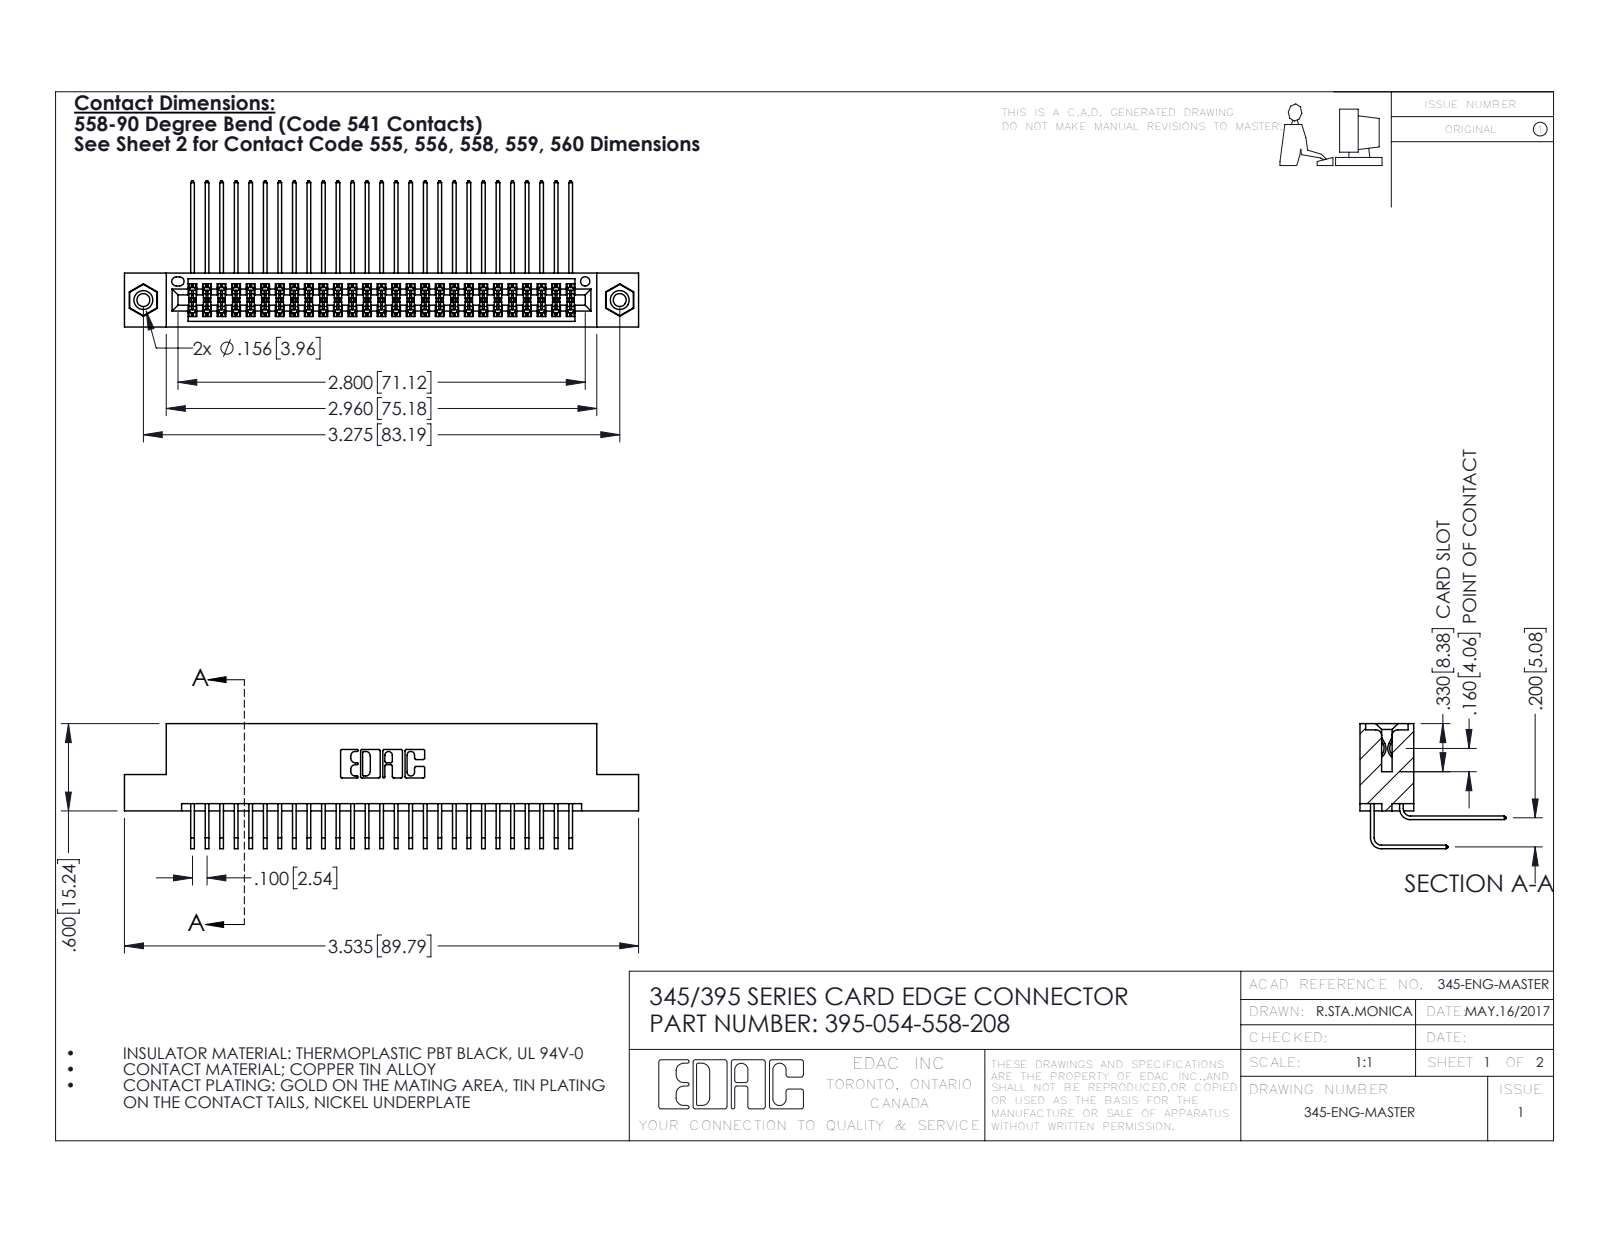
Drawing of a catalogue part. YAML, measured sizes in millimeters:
part_name: "345-292-001_558 Tail - 2; 395-054-558-208; 345 Part_Flush Mounting Lugs - 0.156 Dia-TI; 345-292-001_558 559 Tail - 1 (+1 more)"
step_written_by: "SolidWorks 2016 (CONFIG_CONTROL_DESIGN)"
units: millimeters
bodies: {solids: 57, faces: 2994, planar: 2002, cylindrical: 976, other: 16}
overall_size: [89.8, 25.5, 21.8]
volume: 8880
surface_area: 14320
round_holes:
  - {diameter: 2.3, count: 2}
  - {diameter: 3.2, count: 2}
  - {diameter: 4, count: 2}
  - {diameter: 1.6, count: 1}
round_bosses_or_shafts:
  - {diameter: 3.9, count: 2}
partial_cylinders:
  - {radius: 0.2, count: 82}
  - {radius: 0.3, count: 22}
  - {radius: 0.2, count: 6}
  - {radius: 0.8, count: 6}
  - {radius: 0.7, count: 3}
  - {radius: 0.4, count: 2}
  - {radius: 0.5, count: 2}
  - {radius: 0.6, count: 2}
face_to_face_distances: [5.1, 1.8, 7.6, 9.4, 2.5, 6.9, 0.6, 5.7, 0.6, 7.2]
hole_center_spacings: [6.9, 77.2, 83.2]
